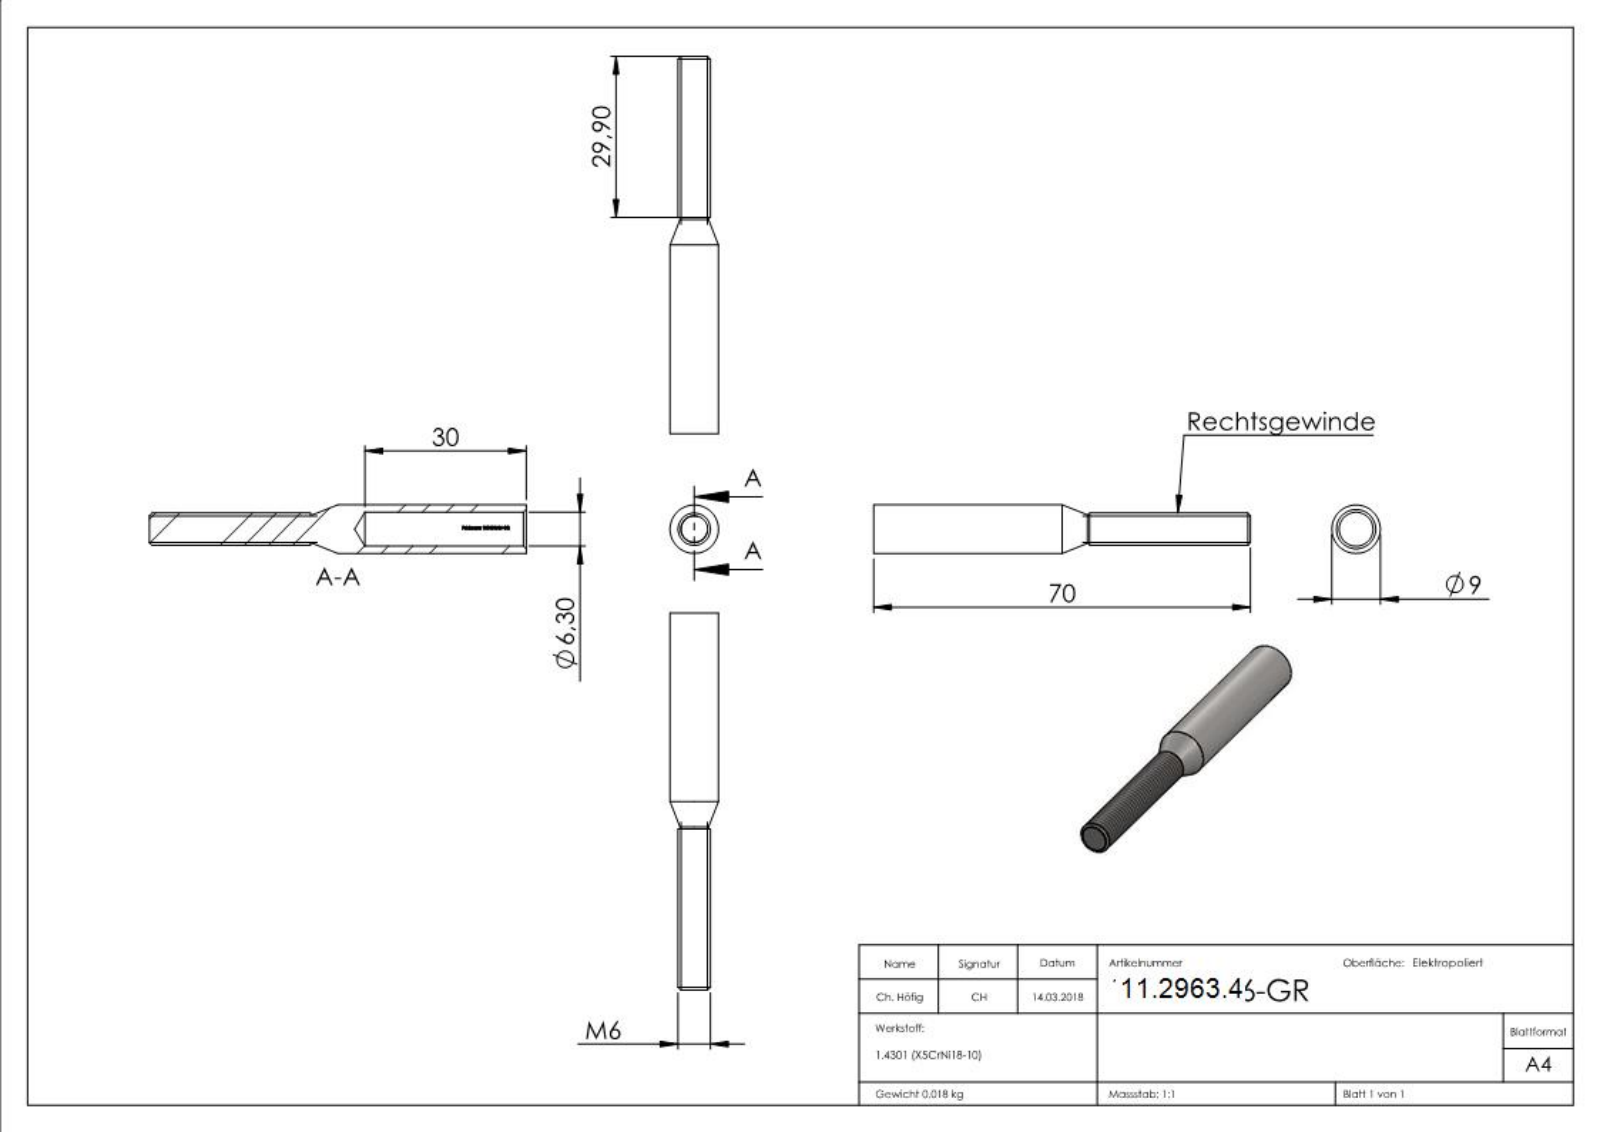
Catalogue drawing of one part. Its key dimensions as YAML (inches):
part_name: "101000606-GR"
step_written_by: "SolidWorks 2015 (CONFIG_CONTROL_DESIGN)"
units: inches
bodies: {solids: 1, faces: 266, planar: 94, cylindrical: 39, other: 133}
overall_size: [2.756, 0.354, 0.354]
volume: 0.141
surface_area: 3.664
round_holes:
  - {diameter: 0.248, count: 1}
round_bosses_or_shafts:
  - {diameter: 0.354, count: 1}
  - {diameter: 0.236, count: 1}
  - {diameter: 0.209, count: 1}
partial_cylinders:
  - {radius: 0.128, count: 1}
face_to_face_distances: [2.756, 1.579, 1.177, 0.032, 0.153, 0.155, 0.327, 0.174, 0.143, 0.185]
